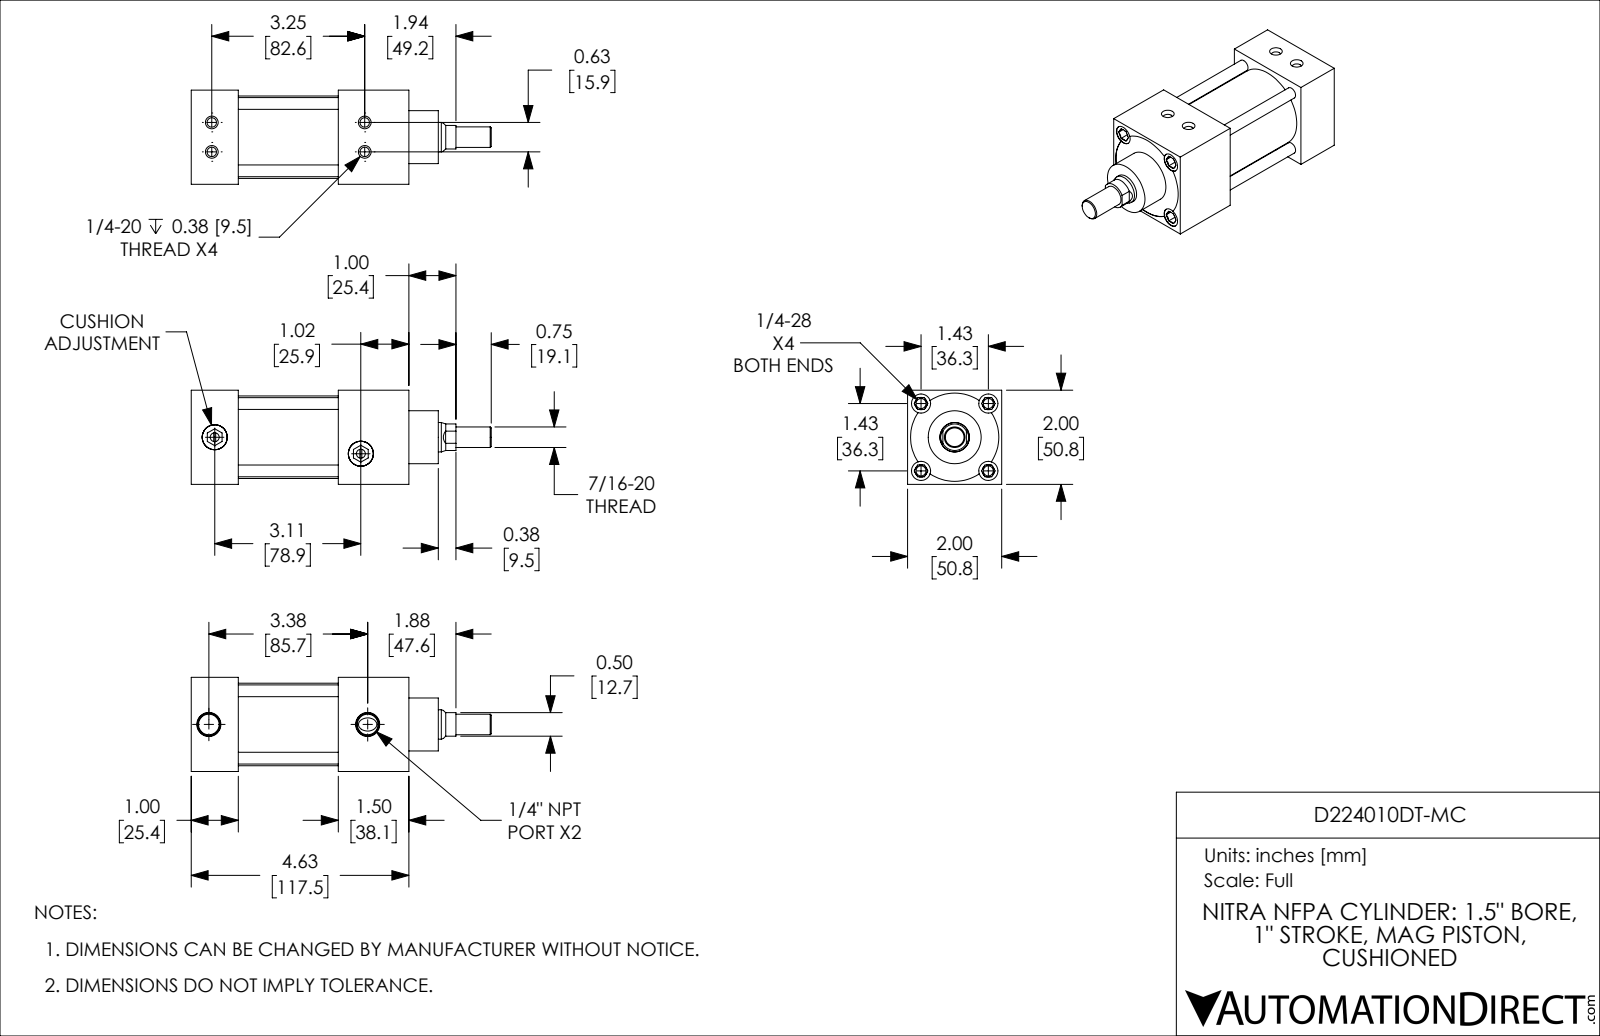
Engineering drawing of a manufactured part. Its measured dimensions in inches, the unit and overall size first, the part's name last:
Units: inches
Overall size (bounding box): 6.375 × 2 × 2
Round holes (diameter × count): ⌀0.201 ×4, ⌀0.213 ×4, ⌀0.406 ×4, ⌀0.19 ×2, ⌀0.438 ×2, ⌀0.531 ×2, ⌀0.626 ×1, ⌀1.501 ×1
Round bosses / shafts (diameter × count): ⌀0.25 ×4, ⌀0.532 ×2, ⌀1.751 ×1, ⌀1.499 ×1, ⌀1.125 ×1, ⌀0.624 ×1, ⌀0.437 ×1
Partial cylindrical surfaces — rounded edges, fillets, slot ends (radius × count): R0.281 ×1, R0.937 ×1
Main face-to-face distances: 2, 1, 3.125, 2.125, 2.125, 4.62, 3.62, 1.495, 1, 1.125
Hole centre spacings: 0.319, 1.011, 1.43, 0.625, 2.022, 3.25, 3.309, 3.327
Volume: 14.31 in³ · Surface area: 94.19 in²
Bodies: 4 solids, 251 faces (90 planar, 81 cylindrical, 80 other)
Part name (STEP PRODUCT): D224010DT-MC_CUSHION; D224010DT-MC_PISTON_KK1; D224010DT-MC; D224010DT-MC_BODY
STEP written by: SolidWorks 2019 (CONFIG_CONTROL_DESIGN)
